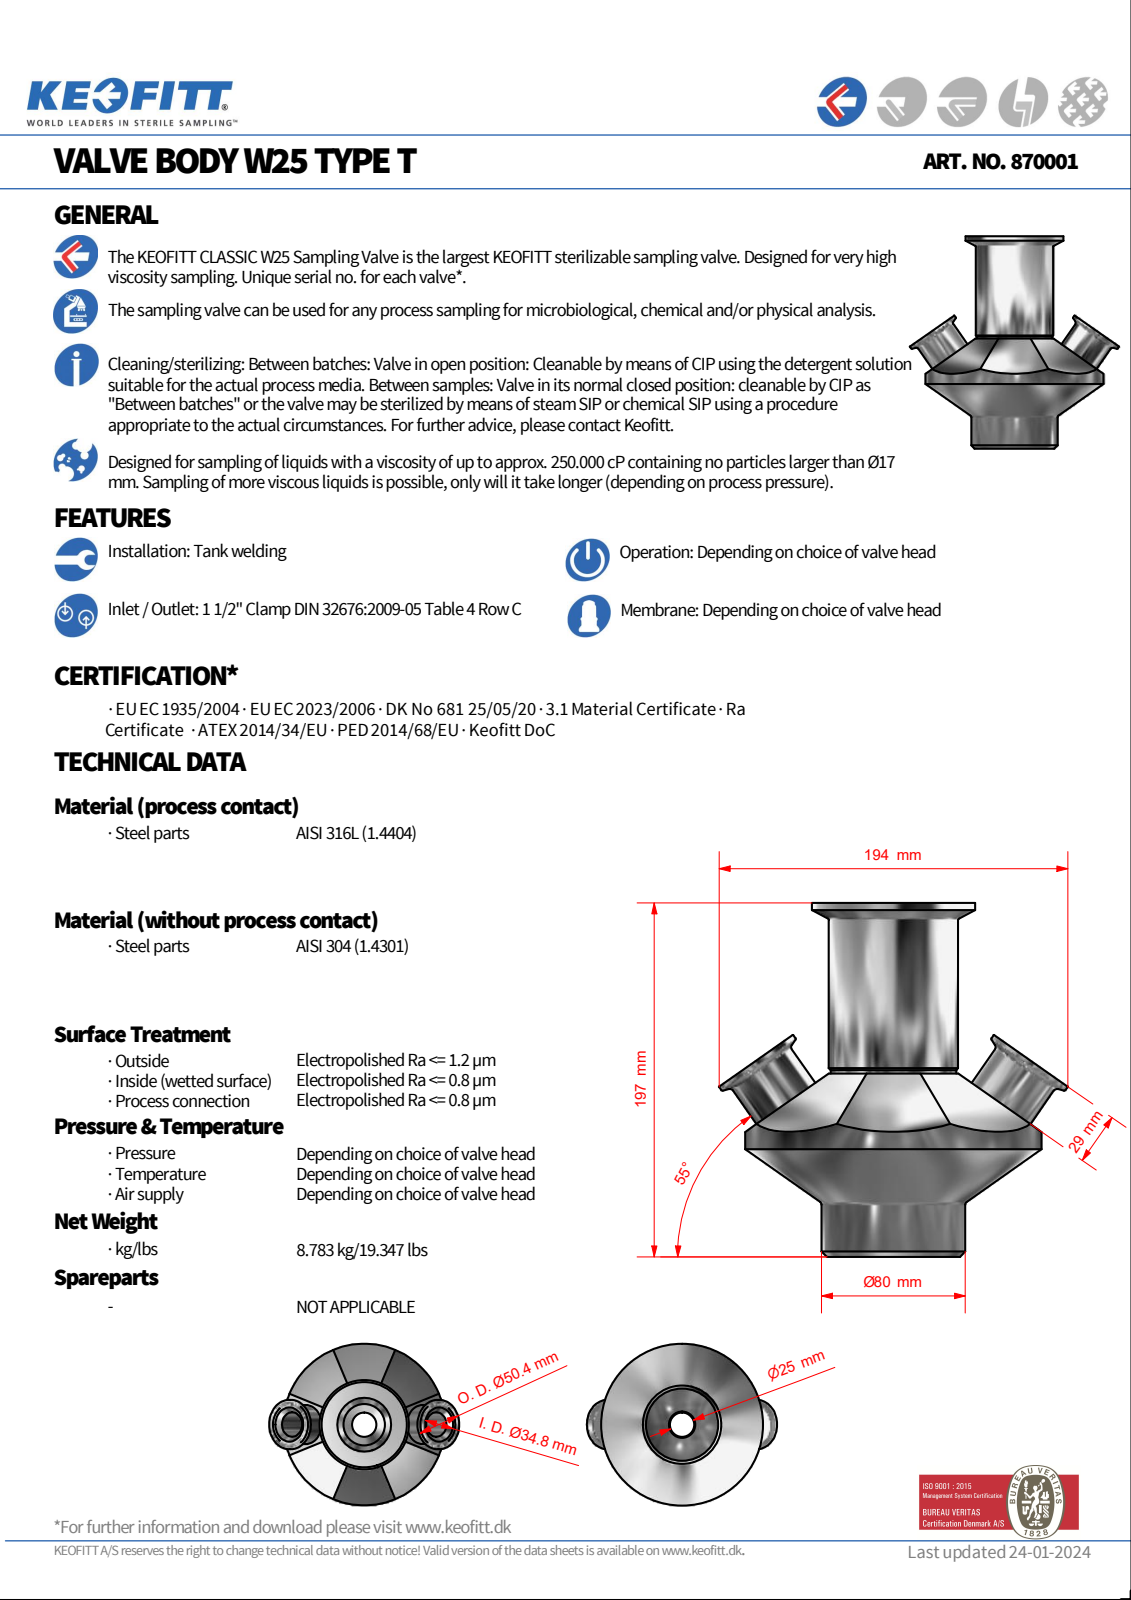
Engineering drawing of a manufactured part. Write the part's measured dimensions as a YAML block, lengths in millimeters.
part_name: "870001; 870001_Simplify_2"
step_written_by: "Autodesk Inventor 2022 (AUTOMOTIVE_DESIGN)"
units: millimeters
bodies: {solids: 2, faces: 59, planar: 18, cylindrical: 13, other: 28}
overall_size: [197, 194.11, 165]
volume: 1635000
surface_area: 111246
round_holes:
  - {diameter: 87.2, count: 1}
round_bosses_or_shafts:
  - {diameter: 50.4, count: 2}
  - {diameter: 40, count: 2}
  - {diameter: 165, count: 1}
  - {diameter: 91, count: 1}
  - {diameter: 80, count: 1}
  - {diameter: 72, count: 1}
  - {diameter: 70, count: 1}
  - {diameter: 65, count: 1}
face_to_face_distances: [92, 102, 194, 85, 17, 109, 29, 197, 112, 95]
